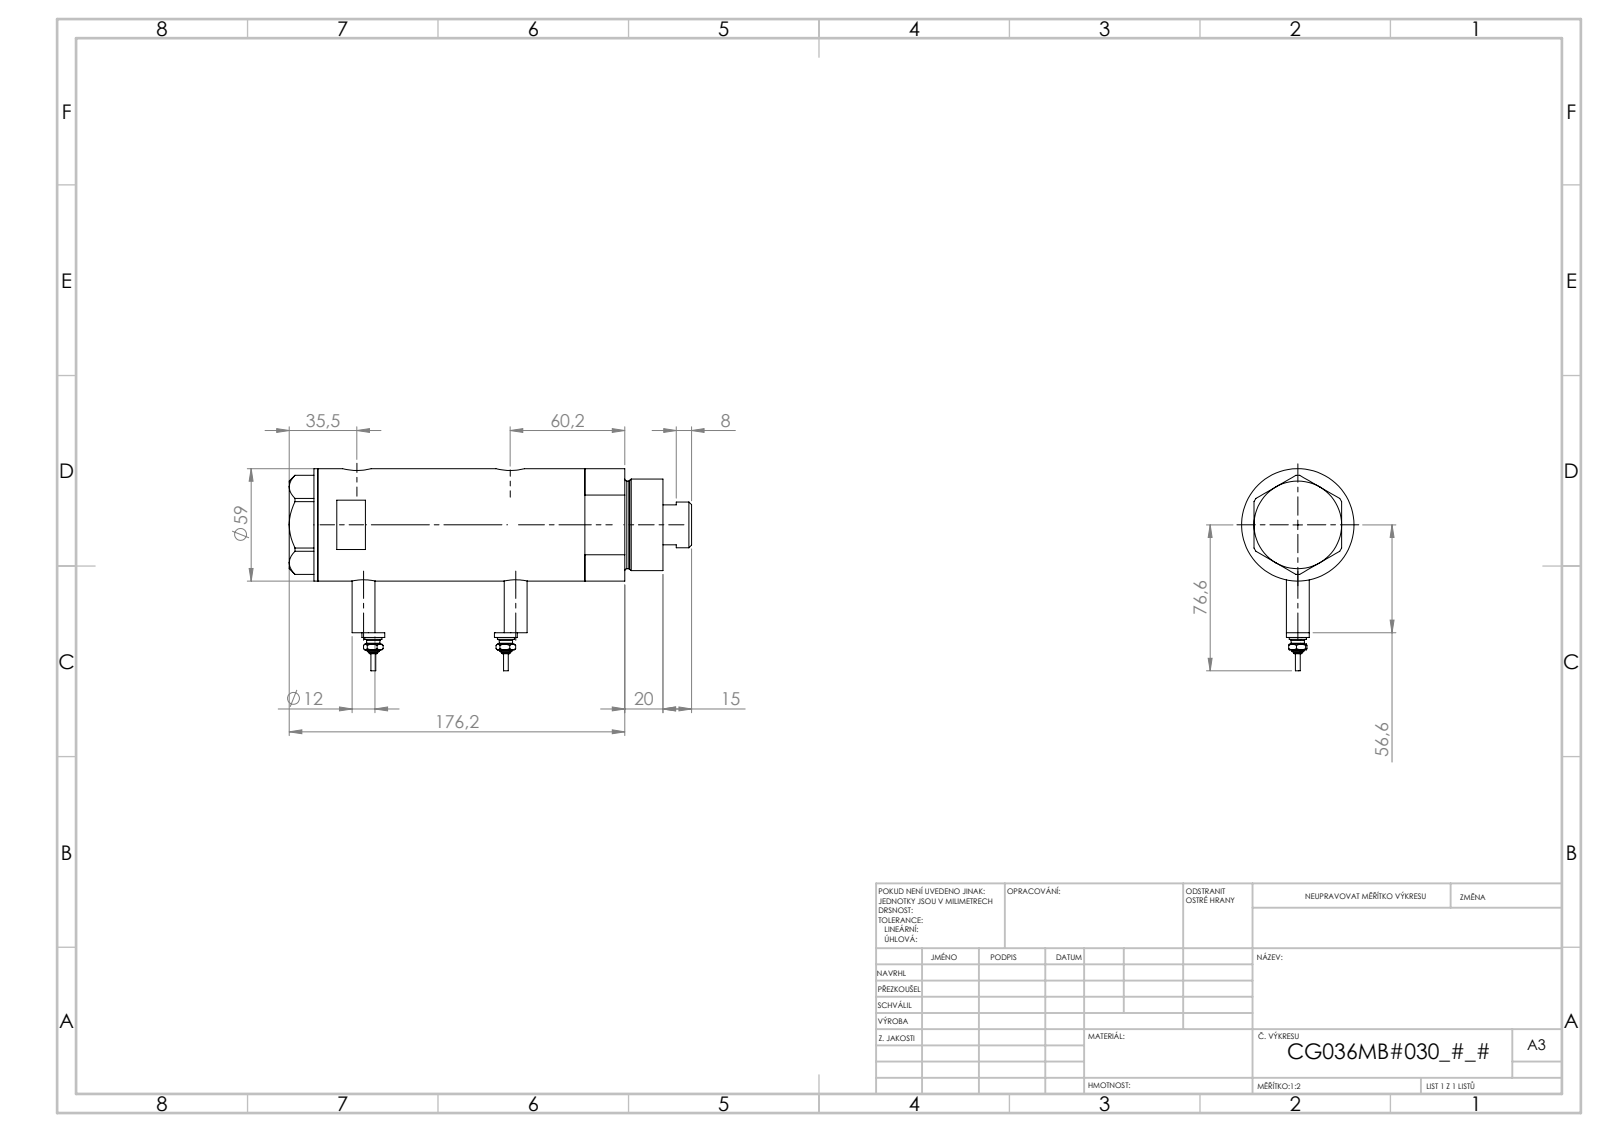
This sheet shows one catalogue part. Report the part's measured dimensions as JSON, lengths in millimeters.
{"part_name": "V270CG_VC; V270CG_BACK; V270CG_MIDDLE; V270CG_FRONT (+1 more)", "step_written_by": "SolidWorks 2019 (CONFIG_CONTROL_DESIGN)", "units": "millimeters", "bodies": {"solids": 6, "faces": 232, "planar": 81, "cylindrical": 77, "other": 74}, "overall_size": [193.42, 91.3, 59], "volume_mm3": 440207, "surface_area_mm2": 95149, "round_holes": [[5, 2], [9.73, 2], [12.5, 2], [15, 2], [8.5, 1], [25, 1], [26.5, 1], [36, 1], [40, 1], [52, 1]], "round_bosses_or_shafts": [[12, 3], [9, 2], [7, 2], [4.34, 2], [2.4, 2], [59, 1], [48, 1], [46, 1]], "face_to_face_distances": [87.34, 23.5, 63.84, 15, 38.5, 102.34, 178.42, 163.42, 139.92, 76.08], "hole_center_spacings": [2.9, 3.5, 62.15, 65.05, 65.65, 68.55, 2.89, 2.91]}
